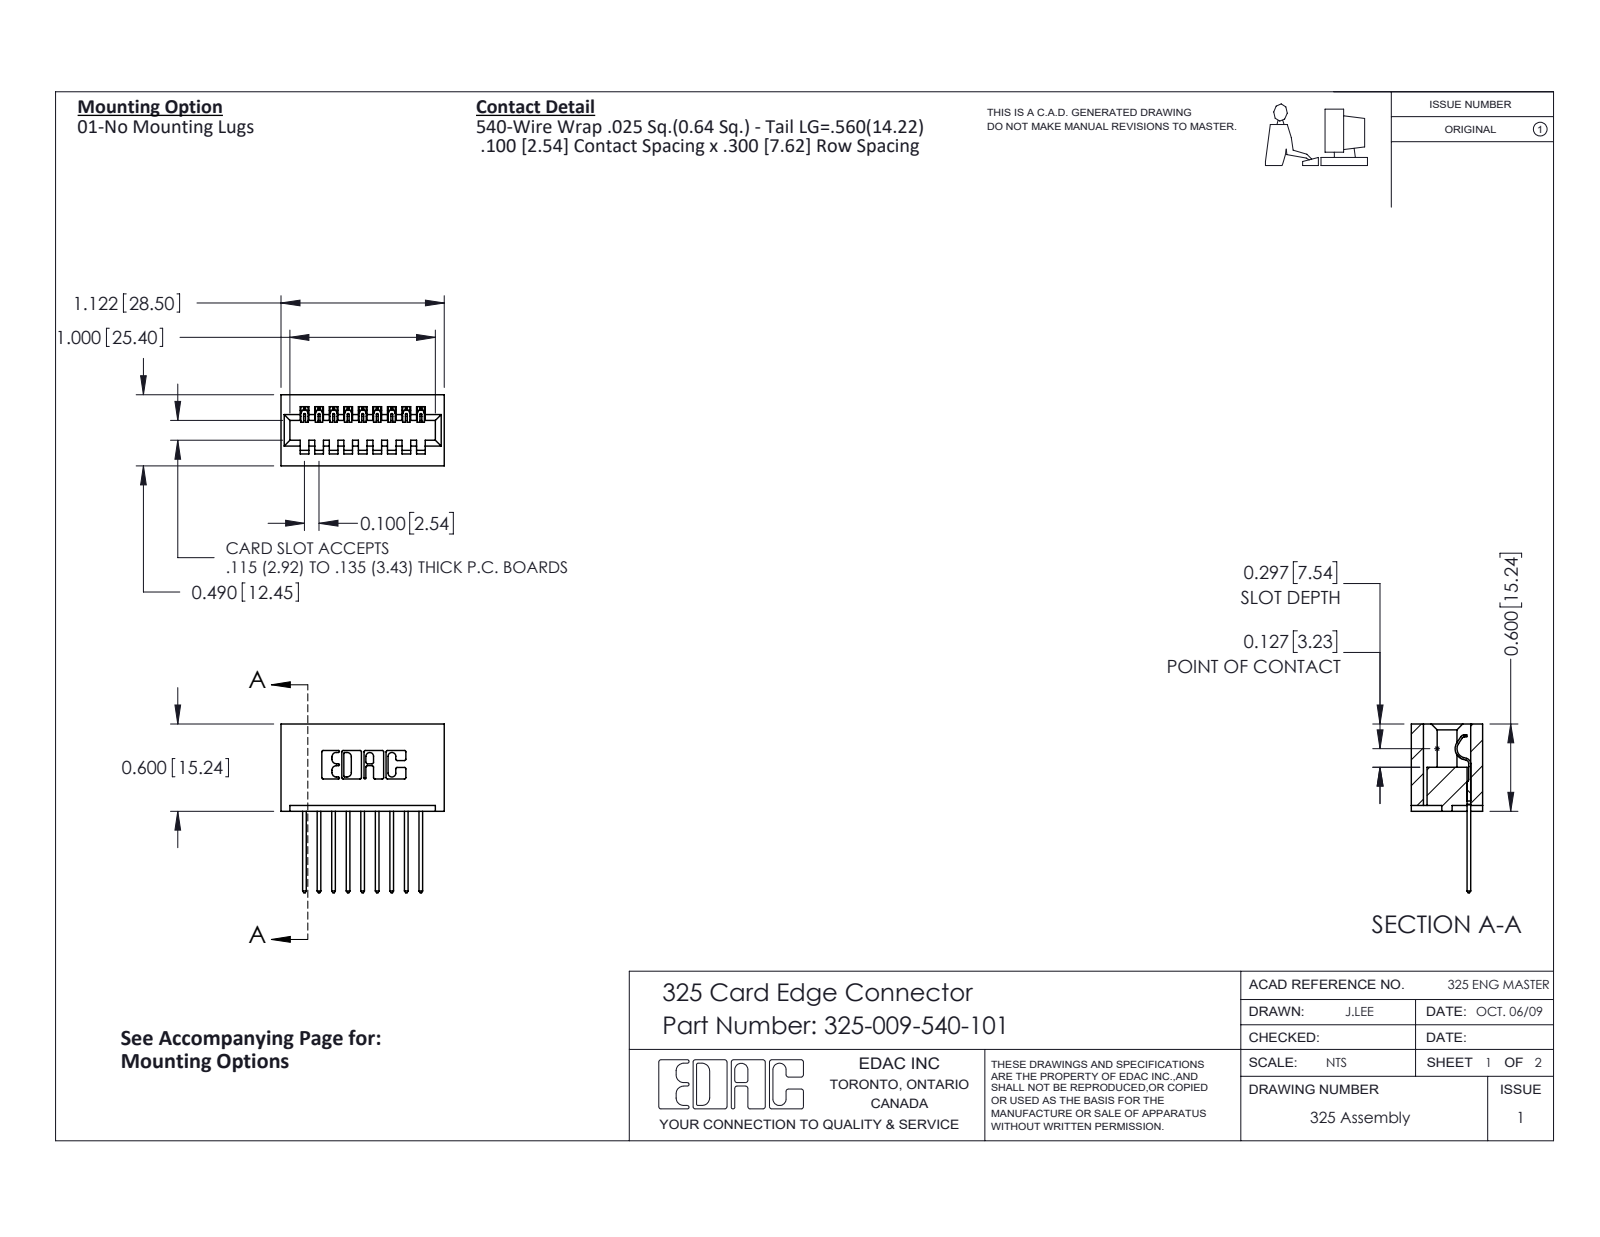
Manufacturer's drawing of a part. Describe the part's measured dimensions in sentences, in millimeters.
The part is named "325-009-540-101; 325 Part_Lugless; 325-292-001_325-293-140". Its 3-D file was written by "SolidWorks 2016 (CONFIG_CONTROL_DESIGN)". It is 10 solids with 628 faces: 444 planar, 184 cylindrical and 0 other. Overall it measures 29.5 by 28.5 by 12.4 millimeters. Its volume is 3 950 cubic millimeters and its surface area 4 328 square millimeters. Partial cylindrical surfaces (rounded edges, fillets, slot ends): 22 of radius 0.3, 18 of radius 0.2, 18 of radius 0.3, 6 of radius 0.2, 6 of radius 0.8, 3 of radius 0.7, 1 of radius 0.4, 1 of radius 0.6. The main face-to-face distances are 7.6, 2.5, 5.1, 2.1, 10.3, 10.2, 1, 1.5, 12.4, 12.7.
